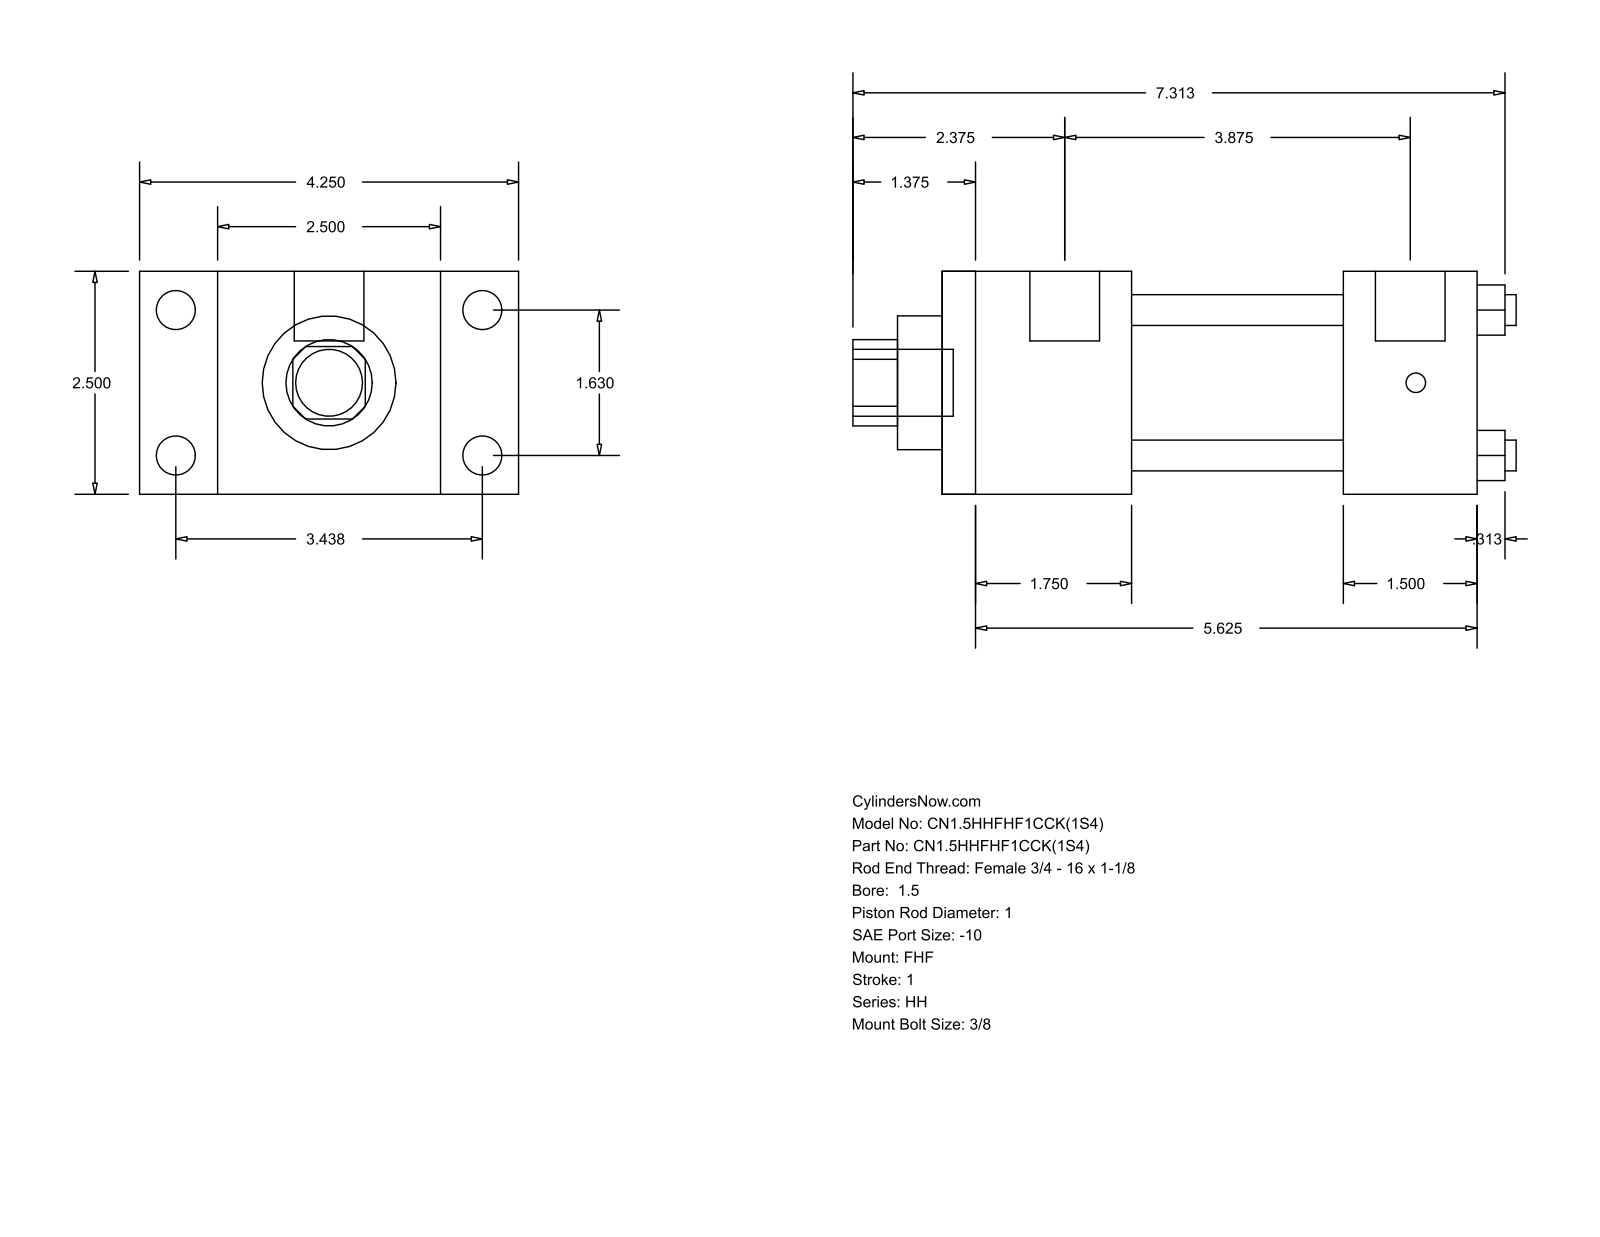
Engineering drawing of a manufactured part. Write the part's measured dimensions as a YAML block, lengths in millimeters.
part_name: "HH_FHF__0150_1"
step_written_by: "GSSL Pune (CONFIG_CONTROL_DESIGN)"
units: millimeters
bodies: {solids: 0, faces: 88, planar: 60, cylindrical: 28, other: 0}
overall_size: [188.91, 107.95, 63.5]
round_holes:
  - {diameter: 8.76, count: 4}
  - {diameter: 25.4, count: 1}
  - {diameter: 38.1, count: 1}
  - {diameter: 44.45, count: 1}
round_bosses_or_shafts:
  - {diameter: 11.13, count: 4}
  - {diameter: 5.56, count: 4}
  - {diameter: 19.84, count: 2}
  - {diameter: 19.05, count: 1}
partial_cylinders:
  - {radius: 12.29, count: 1}
face_to_face_distances: [63.5, 22.23, 85.73, 53.98, 107.96, 152.4, 98.42, 114.3, 60.32, 38.1]
hole_center_spacings: [29.27, 41.4, 58.55]
